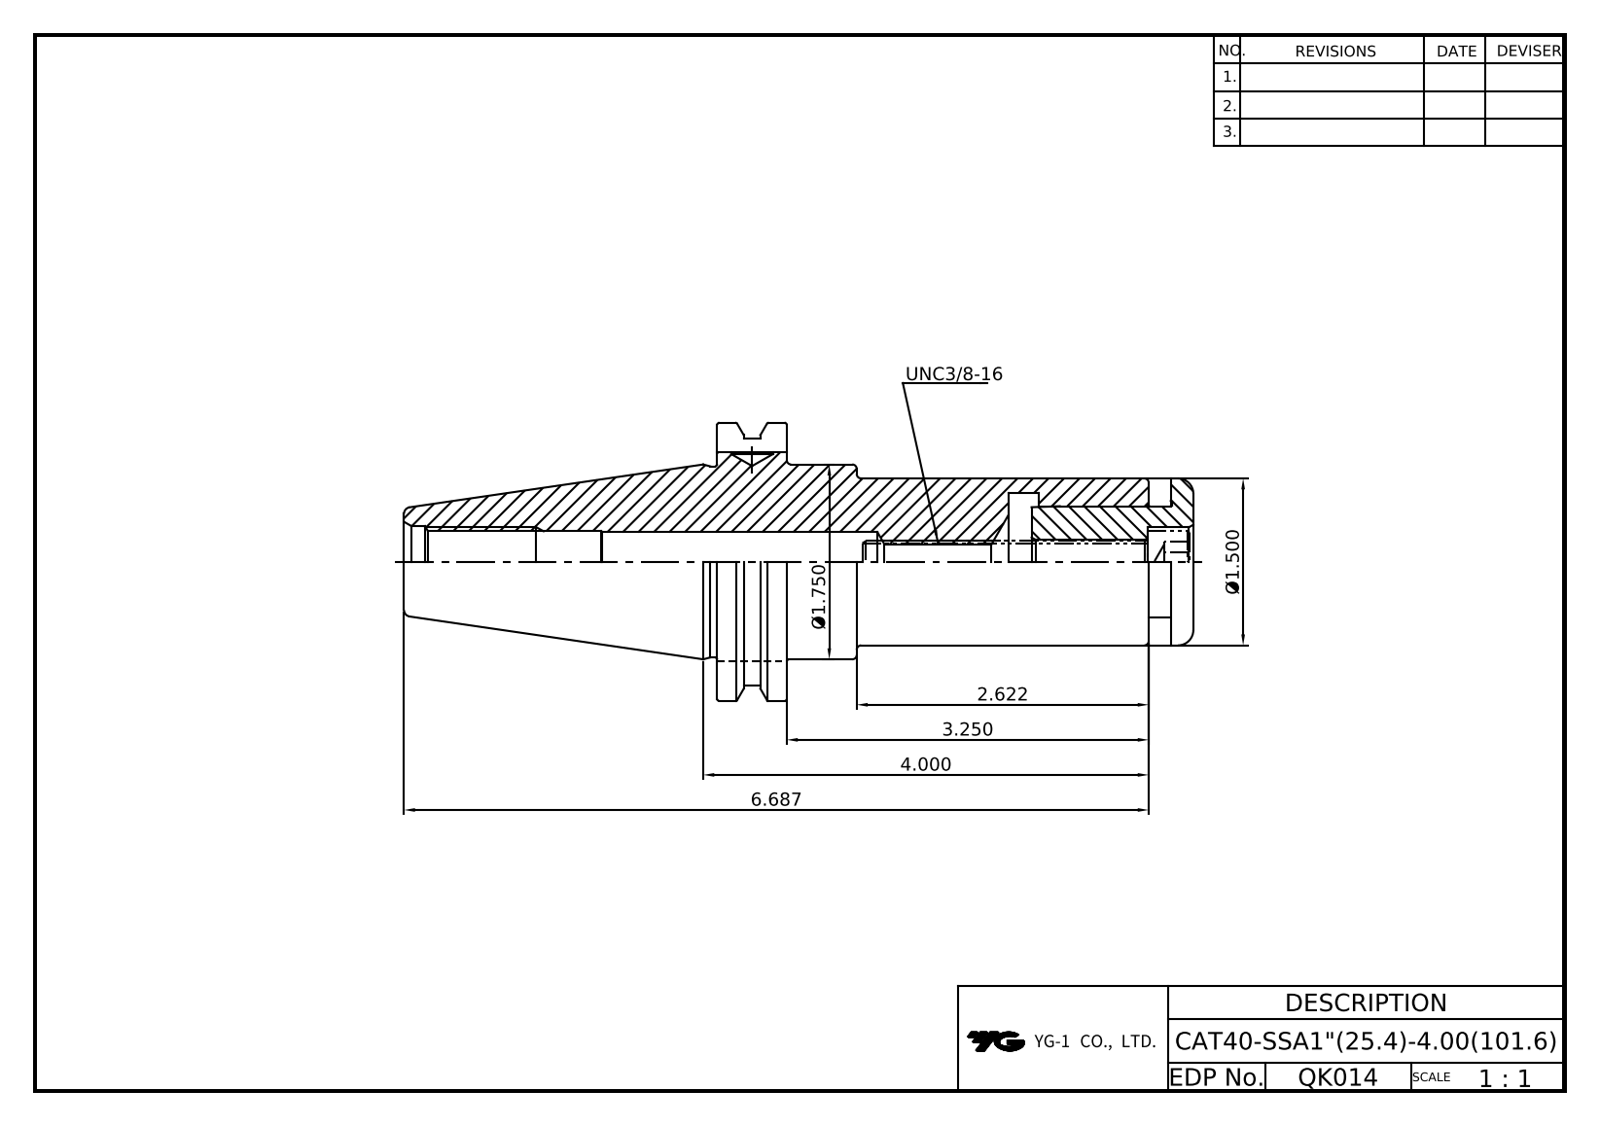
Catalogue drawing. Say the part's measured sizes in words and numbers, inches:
The part is named "LO-CAT40-SSA25.4-101.6; SSH25.4-CAP; SSH25.4-DRIVE KEY; HEX'' WRENCH BOLT-UNC3_8-16x2 1_2L (+1 more)". Its 3-D file was written by "Autodesk Inventor 2025 (AP242_MANAGED_MODEL_BASED_3D_ENGINEERING_MIM_LF)". It is 5 solids with 122 faces: 63 planar, 28 cylindrical and 31 other. Overall it measures 6.89 by 2.5 by 2.405 inches. Its volume is 12.31 cubic inches and its surface area 70.41 square inches. Round holes: 1 of diameter 0.071, 1 of diameter 0.118, 1 of diameter 0.307, 1 of diameter 0.375, 1 of diameter 0.394, 1 of diameter 0.527, 1 of diameter 0.622, 1 of diameter 0.642, 1 of diameter 1, 1 of diameter 1.26. Round bosses or shafts: 1 of diameter 2.5, 1 of diameter 2.217, 1 of diameter 1.75, 1 of diameter 1.717, 1 of diameter 1.5, 1 of diameter 0.984, 1 of diameter 0.562, 1 of diameter 0.375. Partial cylindrical surfaces (rounded edges, fillets, slot ends): 2 of radius 0.125. The main face-to-face distances are 0.625, 3.875, 3.25, 2.615, 1.99, 1.26, 4.078, 3.453, 1.463, 0.203. The hole center spacings are 3.176.
